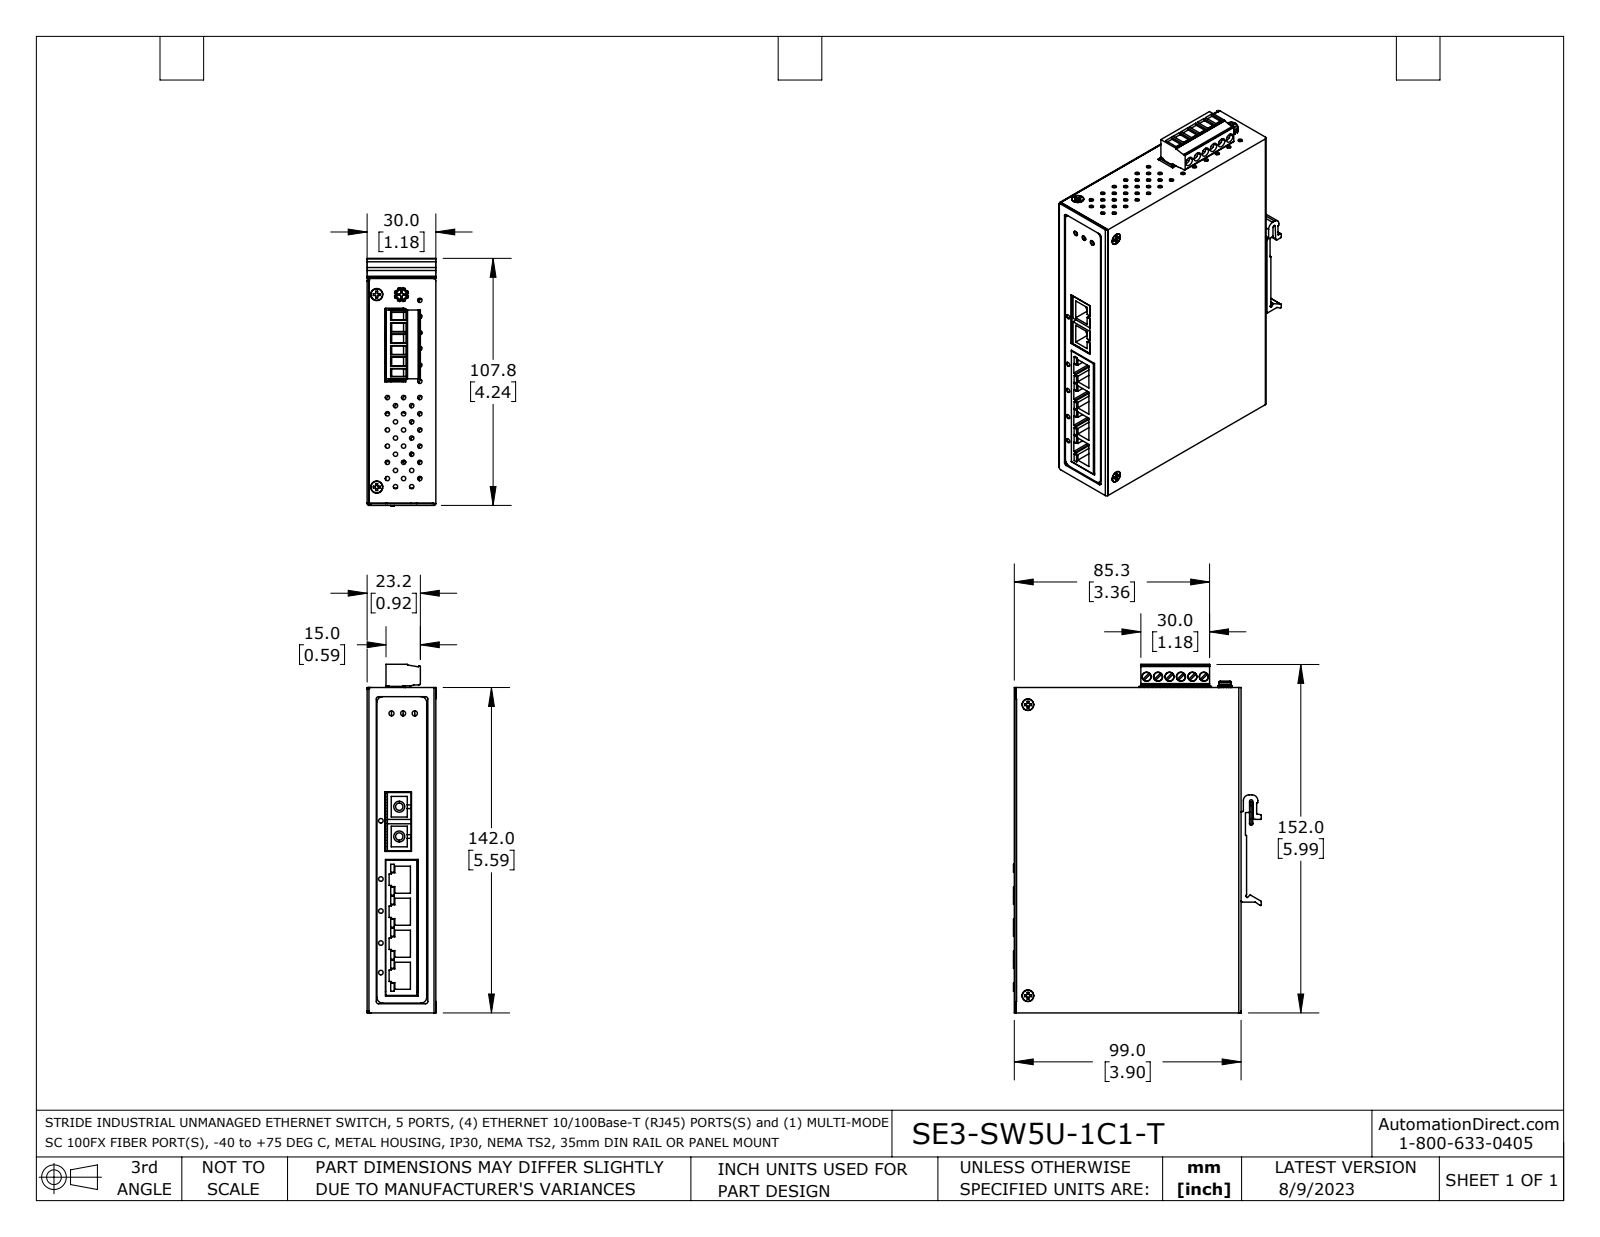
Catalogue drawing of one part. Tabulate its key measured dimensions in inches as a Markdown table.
| quantity | value |
| --- | --- |
| part name | LEONTON_EG2-0800_3D sr1 solid but 16 bad faces1 extTB1ac coord pre CASE MOD for ET2-0502M 1aCd cmb1Cc mm coord fxt |
| STEP written by | SolidWorks 2021 (AUTOMOTIVE_DESIGN) |
| units | inches |
| bodies | 33 solids, 2061 faces (1007 planar, 792 cylindrical, 262 other) |
| overall size | 5.99 × 4.258 × 1.181 |
| volume | 4.126 in³ |
| surface area | 172.3 in² |
| round holes (diameter × count) | 0.075 × 111, 0.098 × 9, 0.157 × 9, 0.079 × 5, 0.097 × 4, 0.118 × 3, 0.087 × 2, 0.096 × 2, 0.096 × 2, 0.126 × 2, 0.197 × 2, 0.209 × 2 |
| round bosses / shafts (diameter × count) | 0.118 × 13, 0.051 × 11, 0.197 × 10, 0.161 × 8, 0.149 × 6, 0.055 × 6, 0.035 × 6, 0.165 × 4 |
| partial cylindrical surfaces (radius × count) | 0.01 × 52, 0.004 × 47, 0.008 × 17, 0.012 × 14, 0.039 × 13, 0.031 × 10, 0.098 × 7, 0.115 × 6 |
| main face-to-face distances | 0.031, 0.039, 1.15, 1.11, 1.142, 1.181, 5.559, 0.02, 0.287, 0.823 |
| hole center spacings | 0.44, 0.278, 0.197, 0.394, 0.557, 0.622, 0.591, 1.148 |
